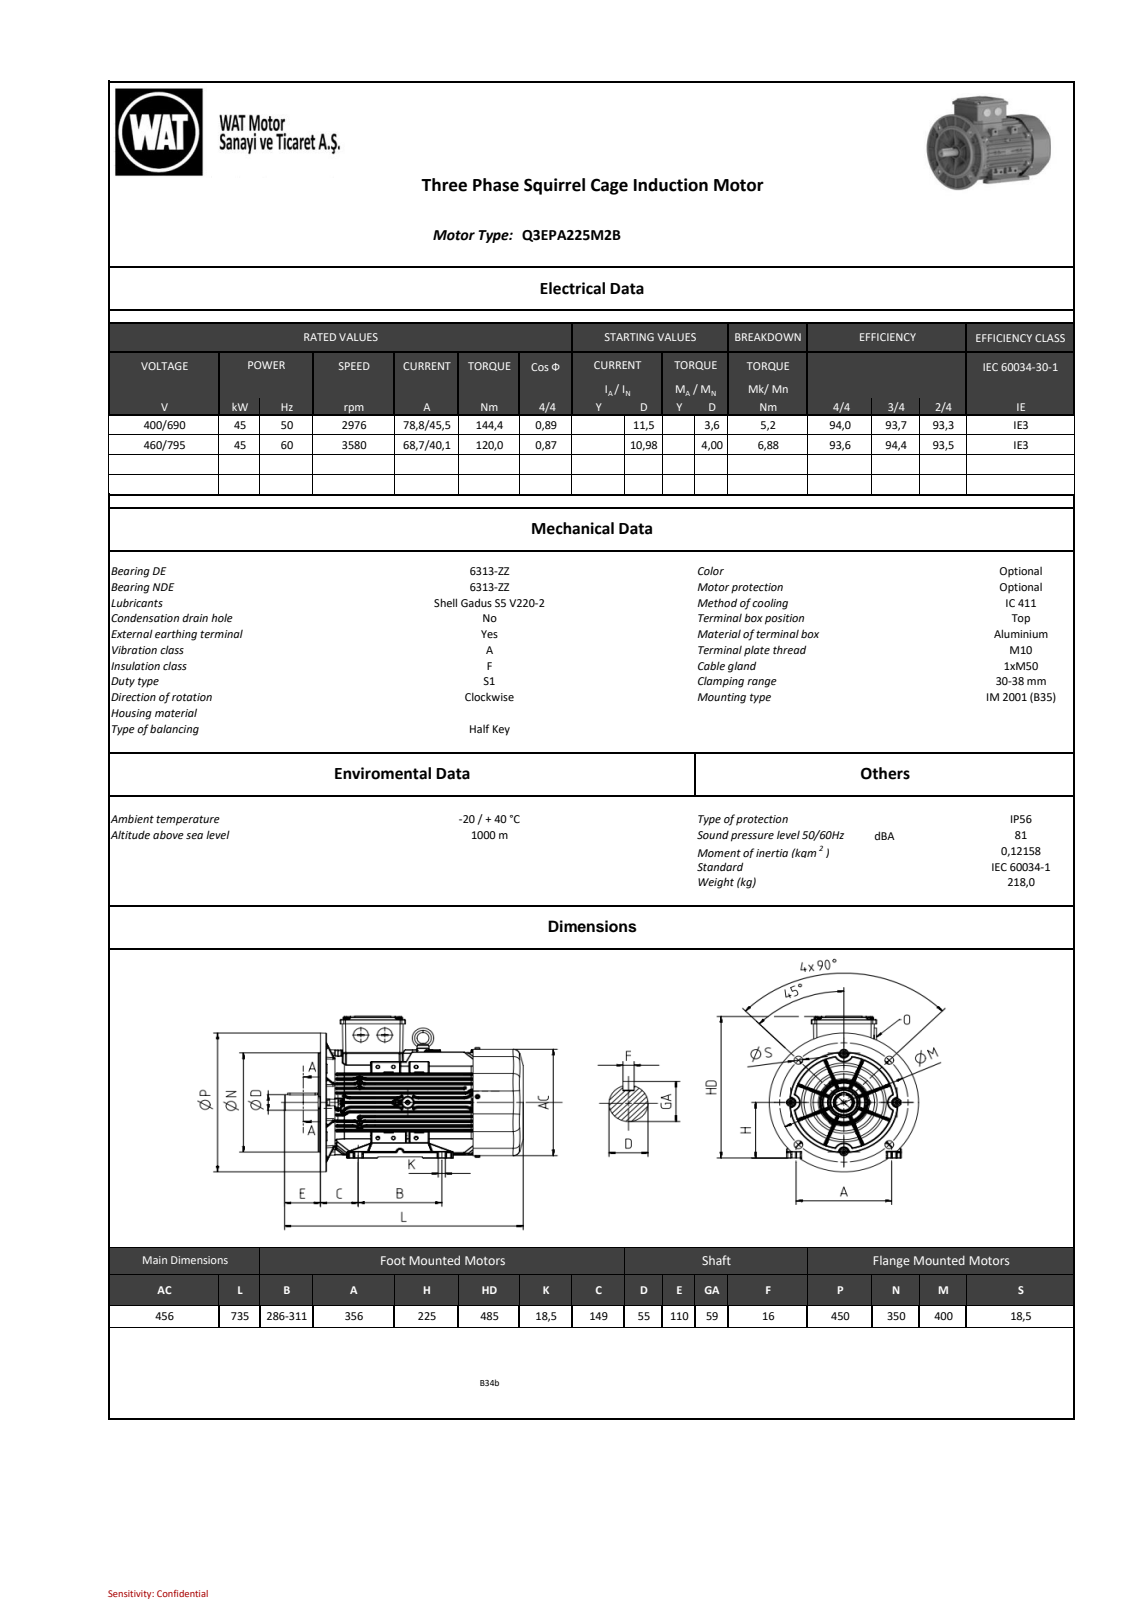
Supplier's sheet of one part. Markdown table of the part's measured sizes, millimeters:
| quantity | value |
| --- | --- |
| part name | AB_objects |
| STEP written by | SIEMENS PLM Software NX2206.8101 (AUTOMOTIVE_DESIGN) |
| units | millimeters |
| bodies | 0 solids, 14651 faces (6454 planar, 2759 cylindrical, 5438 other) |
| overall size | 735 × 507.5 × 450 |
| round holes (diameter × count) | 10.5 × 8, 19 × 8, 0.7 × 6, 6 × 5, 7.5 × 5, 4.3 × 4, 5.5 × 4, 6.5 × 4, 8.38 × 4, 19.5 × 4, 4 × 3, 5 × 3 |
| round bosses / shafts (diameter × count) | 10 × 6, 16.5 × 4, 16 × 4, 5.85 × 3, 58 × 2, 55.1 × 2, 52.3 × 2, 52.2 × 2 |
| partial cylindrical surfaces (radius × count) | 1 × 619, 2 × 444, 0.2 × 332, 0.5 × 154, 5 × 81, 2.5 × 76, 3 × 48, 4 × 48 |
| main face-to-face distances | 189.81, 15.53, 169.04, 20.77, 14.83, 5.24, 184.57, 24.63, 150.23, 39.58 |
| hole center spacings | 7.4, 156, 146.34, 282.85, 68.18, 82.67, 200.01, 231.52 |
